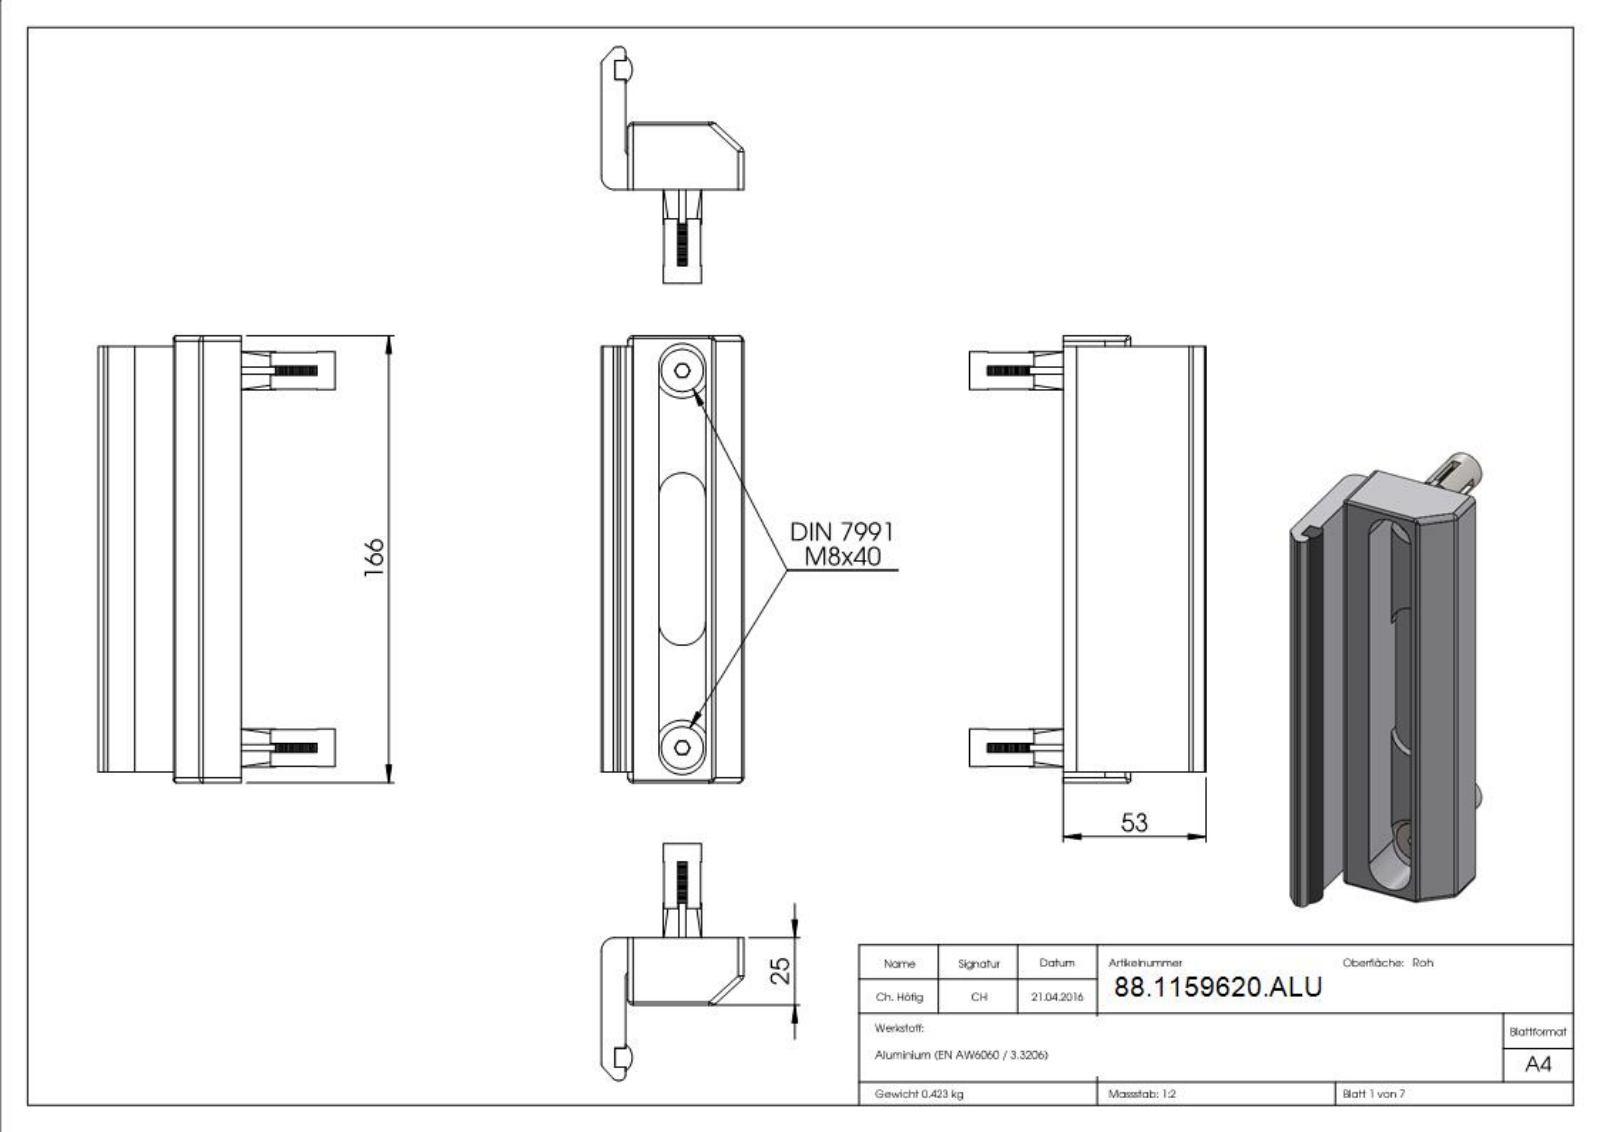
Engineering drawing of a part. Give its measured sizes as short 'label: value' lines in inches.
name: 59620-ALU Teil4; 59620-ALU; 59620-ALU Teil5; 59620-ALU Teil2 (+4 more)
written by: SolidWorks 2018 (CONFIG_CONTROL_DESIGN)
unit: in
bodies: 9 solids, 771 faces (441 planar, 98 cylindrical, 232 other)
size: 6.535 × 3.459 × 2.08
volume: 9.339 in³; area: 131.4 in²
holes: 2× ⌀0.197, 2× ⌀0.268, 2× ⌀0.321, 2× ⌀0.453
bosses: 2× ⌀0.613, 2× ⌀0.551, 2× ⌀0.315
rounds: 14× R0.079, 4× R0.344, 3× R0.197, 2× R0.039, 1× R0.246
face distances: 0.079, 0.15, 0.354, 1.614, 0.709, 0.157, 0.984, 0.8, 0.446, 0.039
hole spacings: 0.954, 4.732, 3.898, 5.512
